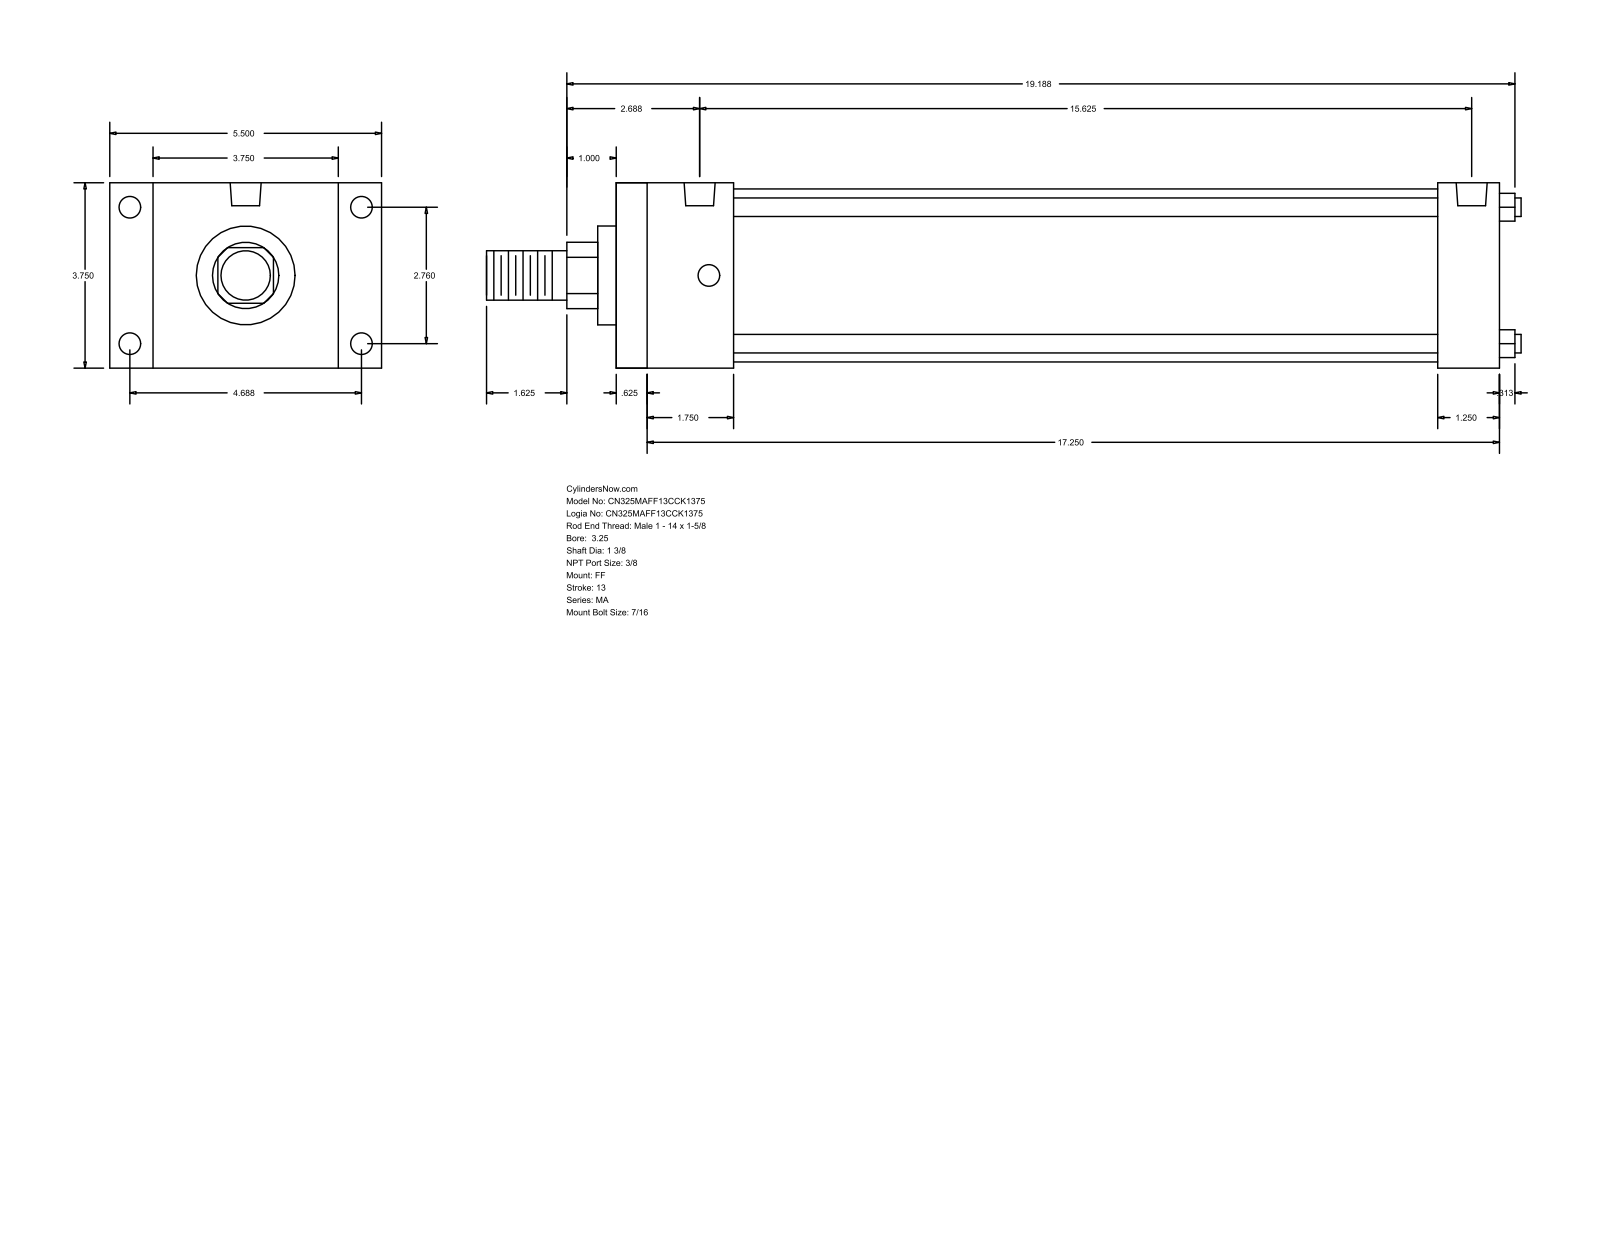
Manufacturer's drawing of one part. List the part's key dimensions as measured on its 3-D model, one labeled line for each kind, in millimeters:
Part name (STEP PRODUCT): MA_FF__0325_1.375
STEP written by: GSSL Pune (CONFIG_CONTROL_DESIGN)
Units: millimetres
Bodies: 0 solids, 92 faces (64 planar, 28 cylindrical, 0 other)
Overall size (bounding box): 531.81 × 139.7 × 95.25
Round holes (diameter × count): ⌀11.11 ×8, ⌀15.93 ×2
Round bosses / shafts (diameter × count): ⌀9.53 ×4, ⌀88.9 ×1, ⌀50.8 ×1, ⌀34.92 ×1, ⌀25.4 ×1
Partial cylindrical surfaces — rounded edges, fillets, slot ends (radius × count): R17.06 ×1
Main face-to-face distances: 95.24, 454.03, 15.87, 438.16, 22.23, 117.47, 60.32, 422.28, 44.45, 406.41
Hole centre spacings: 70.1, 119.06, 138.16, 387.35, 4.76, 4.77, 392.11, 392.12
